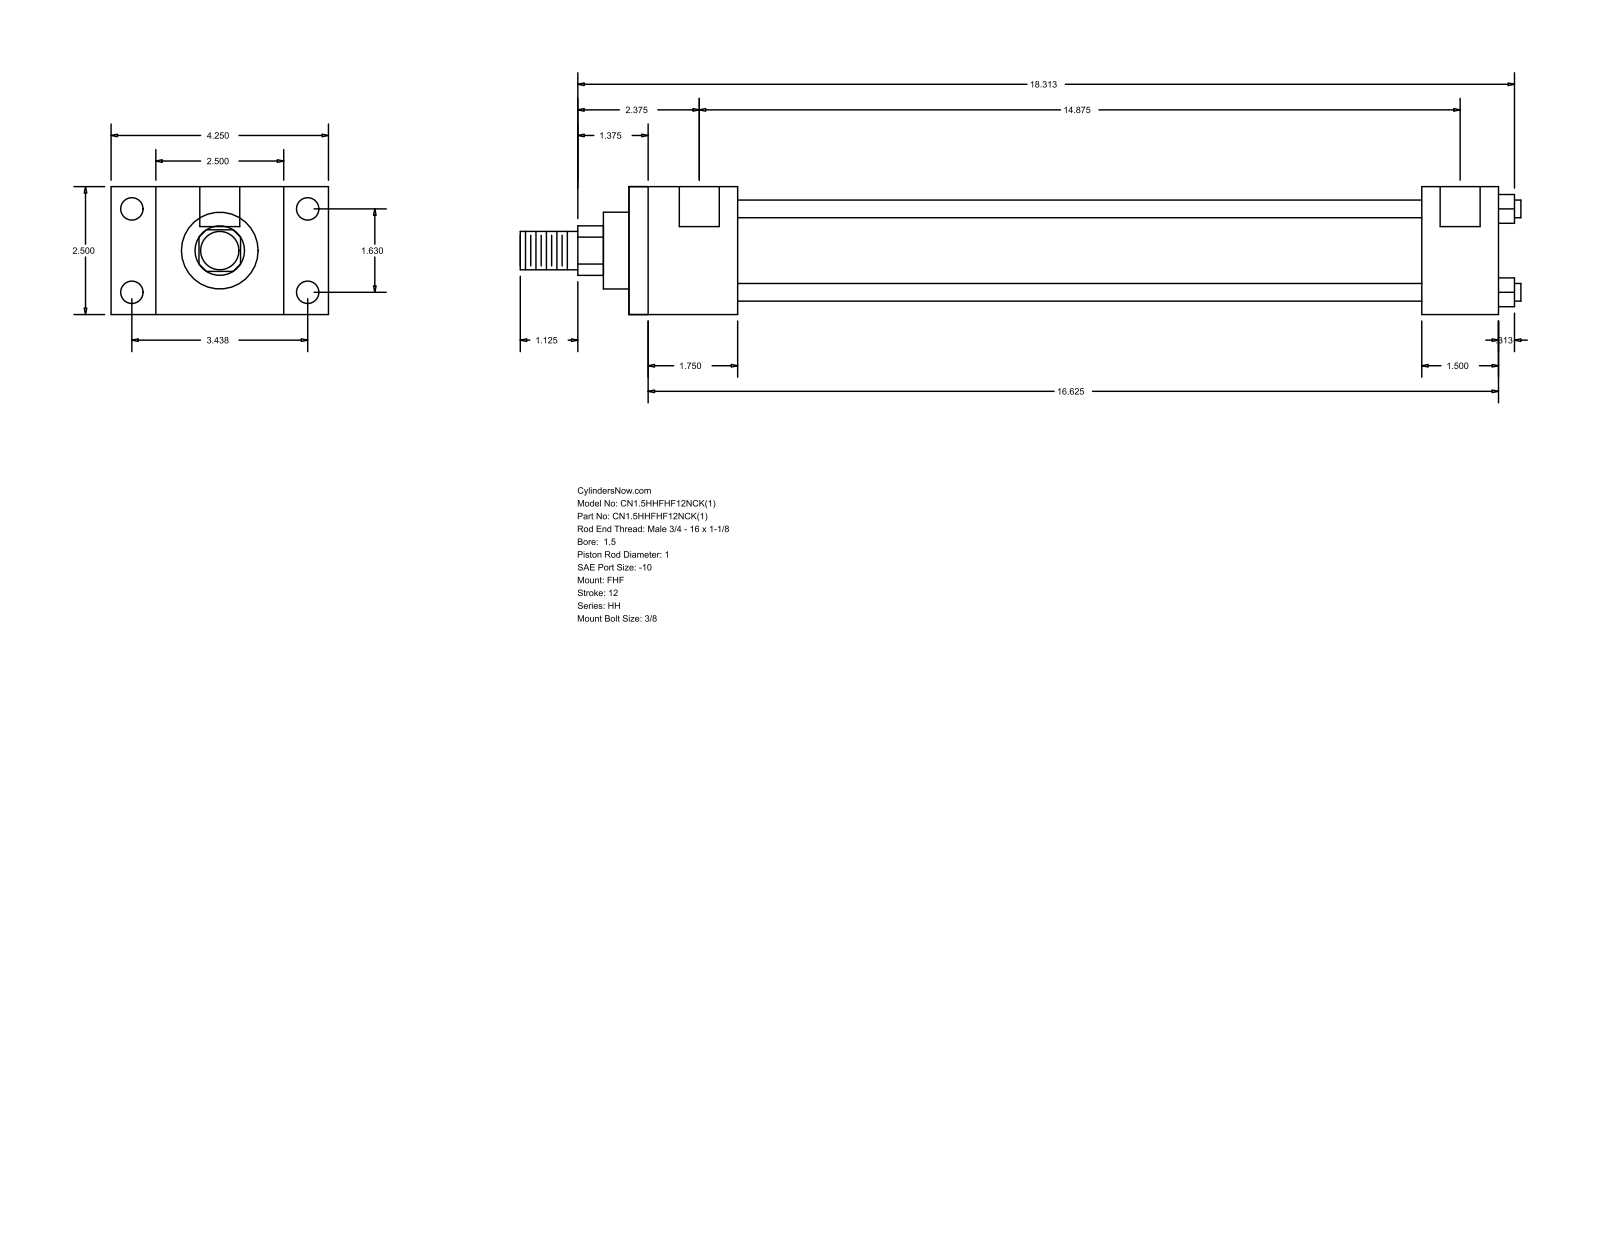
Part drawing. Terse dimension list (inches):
name: HH_FHF__0150_1
written by: GSSL Pune (CONFIG_CONTROL_DESIGN)
unit: in
bodies: 0 solids, 88 faces (60 planar, 28 cylindrical, 0 other)
size: 19.563 × 4.25 × 2.5
holes: 4× ⌀0.219, 4× ⌀0.438, 2× ⌀0.781
bosses: 4× ⌀0.345, 1× ⌀1.75, 1× ⌀1.5, 1× ⌀1, 1× ⌀0.75
rounds: 1× R0.484
face distances: 2.5, 0.875, 3.375, 2.125, 4.25, 17, 14.875, 1.5, 15.5, 13.375
hole spacings: 0.063, 1.63, 3.438, 3.805, 14.937, 15, 14.875
